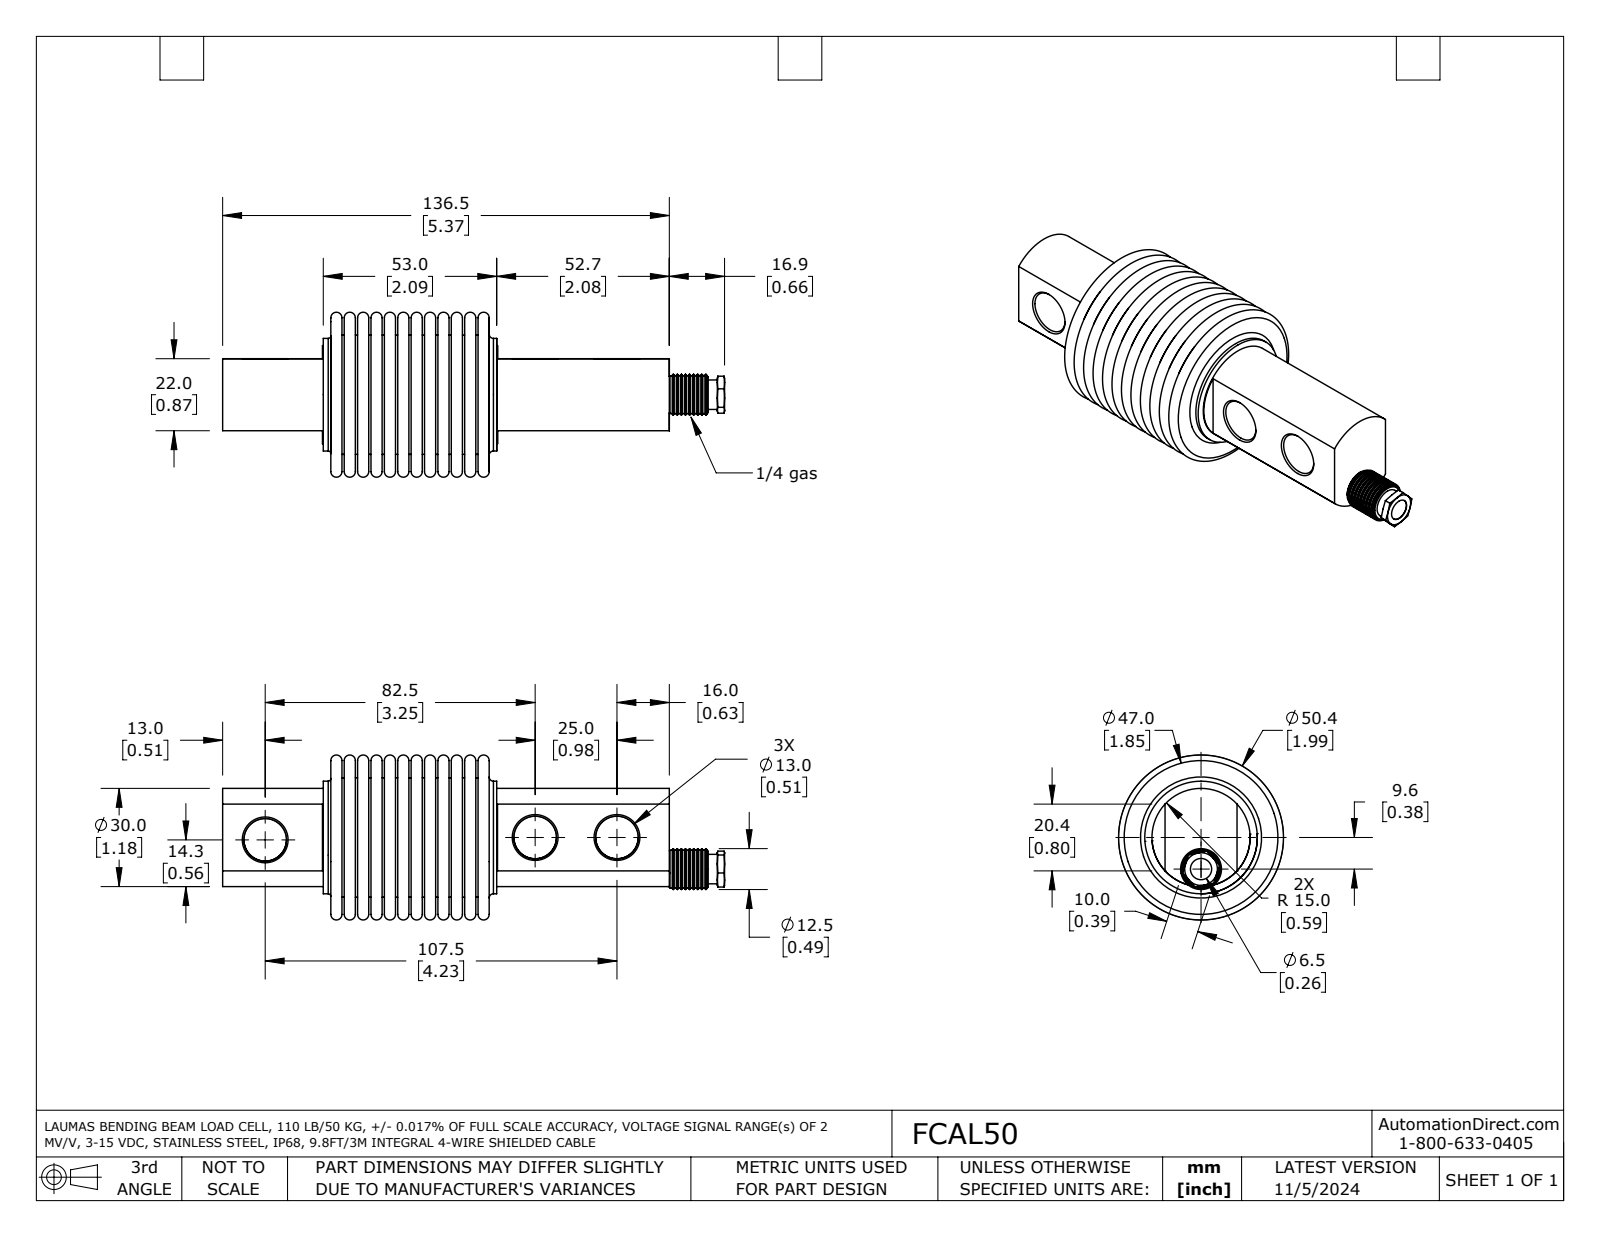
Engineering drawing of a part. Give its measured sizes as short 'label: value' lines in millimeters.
name: FCAL50
written by: SolidWorks 2021 (AUTOMOTIVE_DESIGN)
unit: mm
bodies: 2 solids, 378 faces (32 planar, 30 cylindrical, 316 other)
size: 153.4 × 50.4 × 50.4
volume: 86 880 mm³; area: 75 610 mm²
holes: 3× ⌀13, 1× ⌀6.5, 1× ⌀10
bosses: 1× ⌀34.4, 1× ⌀34, 1× ⌀30, 1× ⌀11.5, 1× ⌀9
face distances: 48.2, 22, 48, 48.4, 103.4, 103.3, 55.2, 55, 33.1, 33.2
hole spacings: 25, 82.5, 107.5
